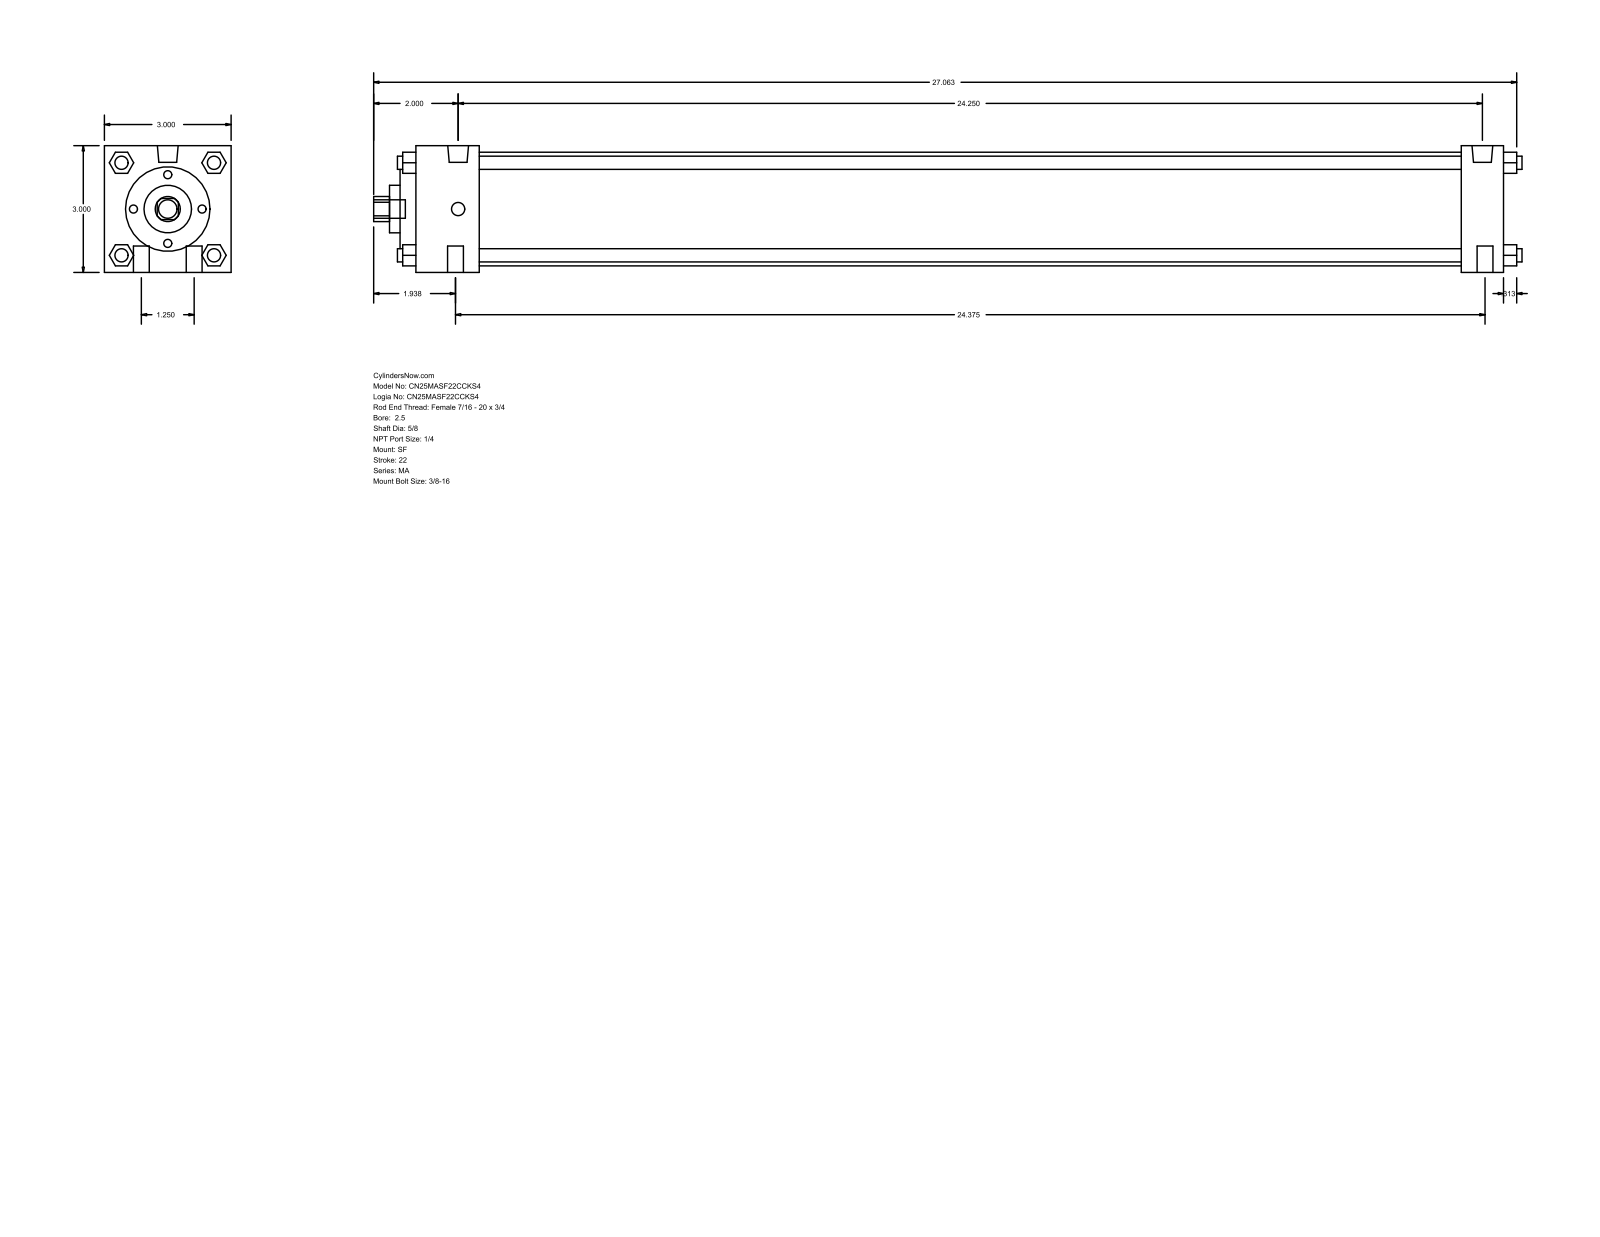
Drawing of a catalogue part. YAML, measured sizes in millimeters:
part_name: "MA_SF__0250_0.625"
step_written_by: "GSSL Pune (CONFIG_CONTROL_DESIGN)"
units: millimeters
bodies: {solids: 0, faces: 126, planar: 95, cylindrical: 31, other: 0}
overall_size: [690.56, 76.2, 76.2]
round_holes:
  - {diameter: 15.88, count: 1}
  - {diameter: 28.57, count: 1}
  - {diameter: 50.8, count: 1}
  - {diameter: 68.33, count: 1}
round_bosses_or_shafts:
  - {diameter: 7.94, count: 6}
  - {diameter: 9.53, count: 4}
  - {diameter: 12.49, count: 2}
  - {diameter: 11.11, count: 1}
partial_cylinders:
  - {radius: 7.54, count: 1}
face_to_face_distances: [76.2, 654.05, 25.4, 628.65, 38.1, 590.55, 615.95, 12.7, 9.52, 47.62]
